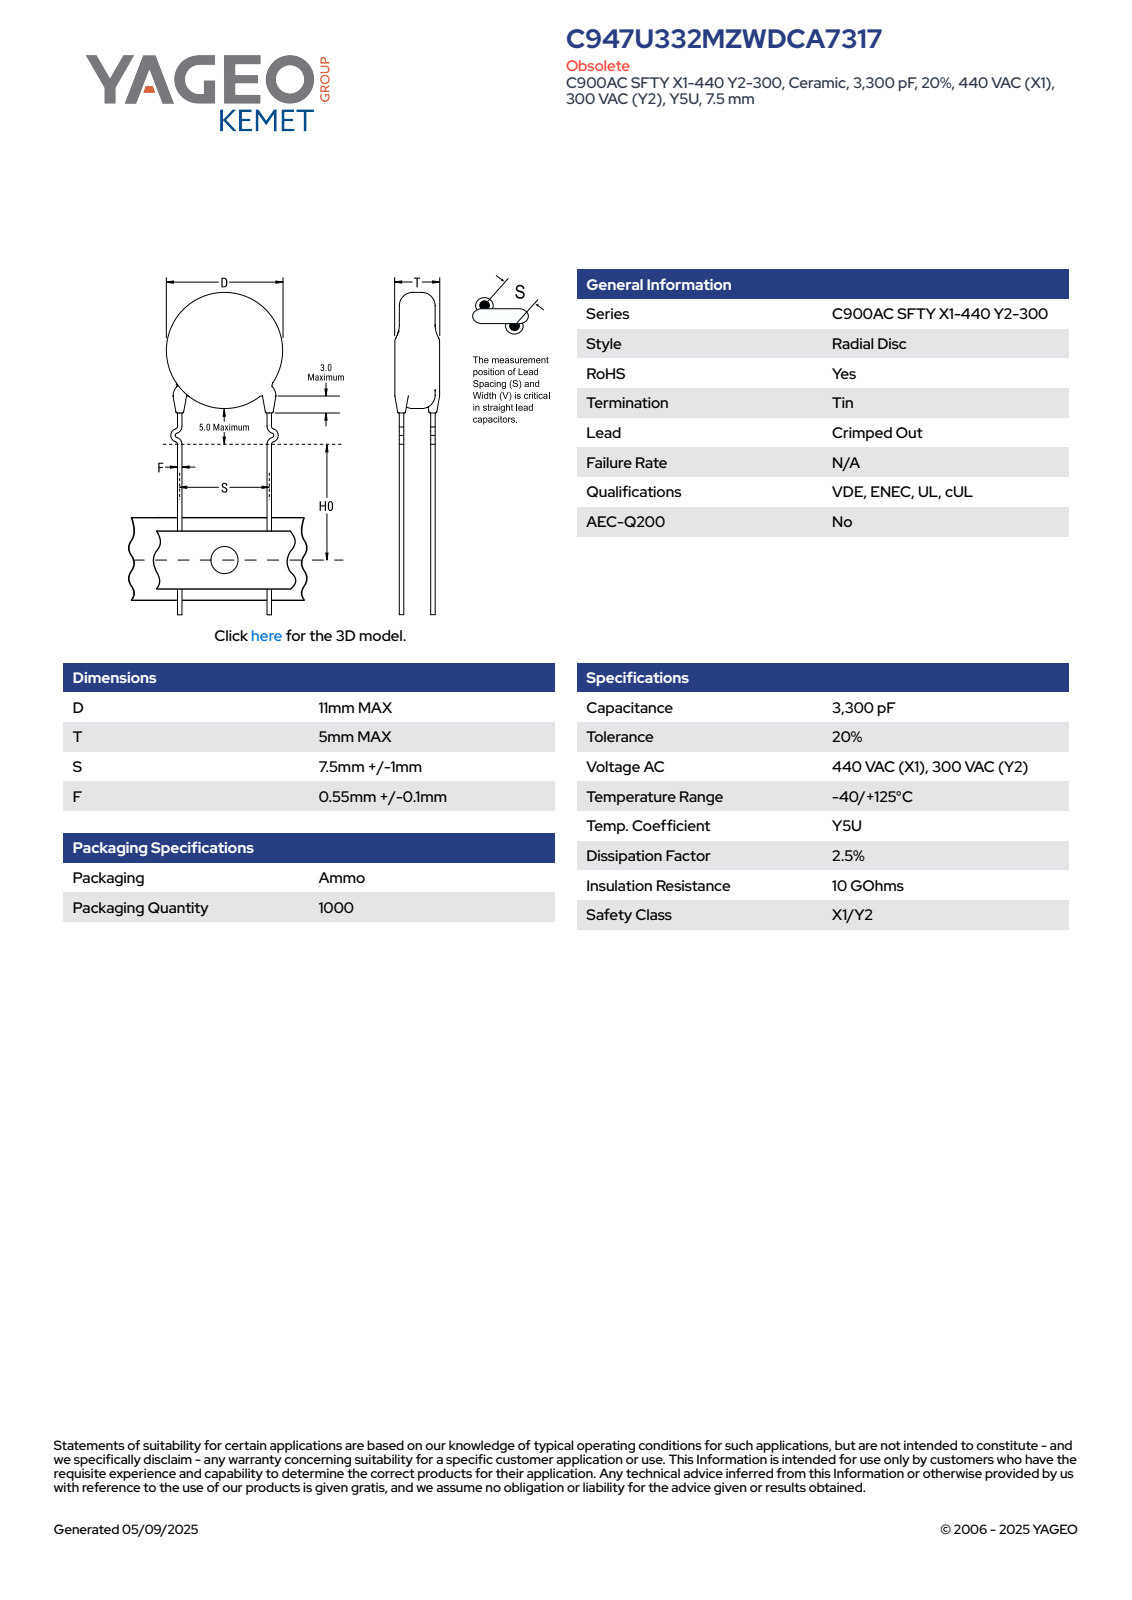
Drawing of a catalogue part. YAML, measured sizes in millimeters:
part_name: "CCD_KCOC900_D11T5S7.5LL20F0.55"
step_written_by: "SolidWorks 2014 (AUTOMOTIVE_DESIGN)"
units: millimeters
bodies: {solids: 4, faces: 85, planar: 63, cylindrical: 6, other: 16}
overall_size: [36, 12.55, 5]
volume: 482
surface_area: 462
round_bosses_or_shafts:
  - {diameter: 1.2, count: 2}
  - {diameter: 11, count: 1}
face_to_face_distances: [5, 1.14, 6.08, 4.94, 0.32, 0.92, 4.67, 2.36, 3.39, 3.53]
